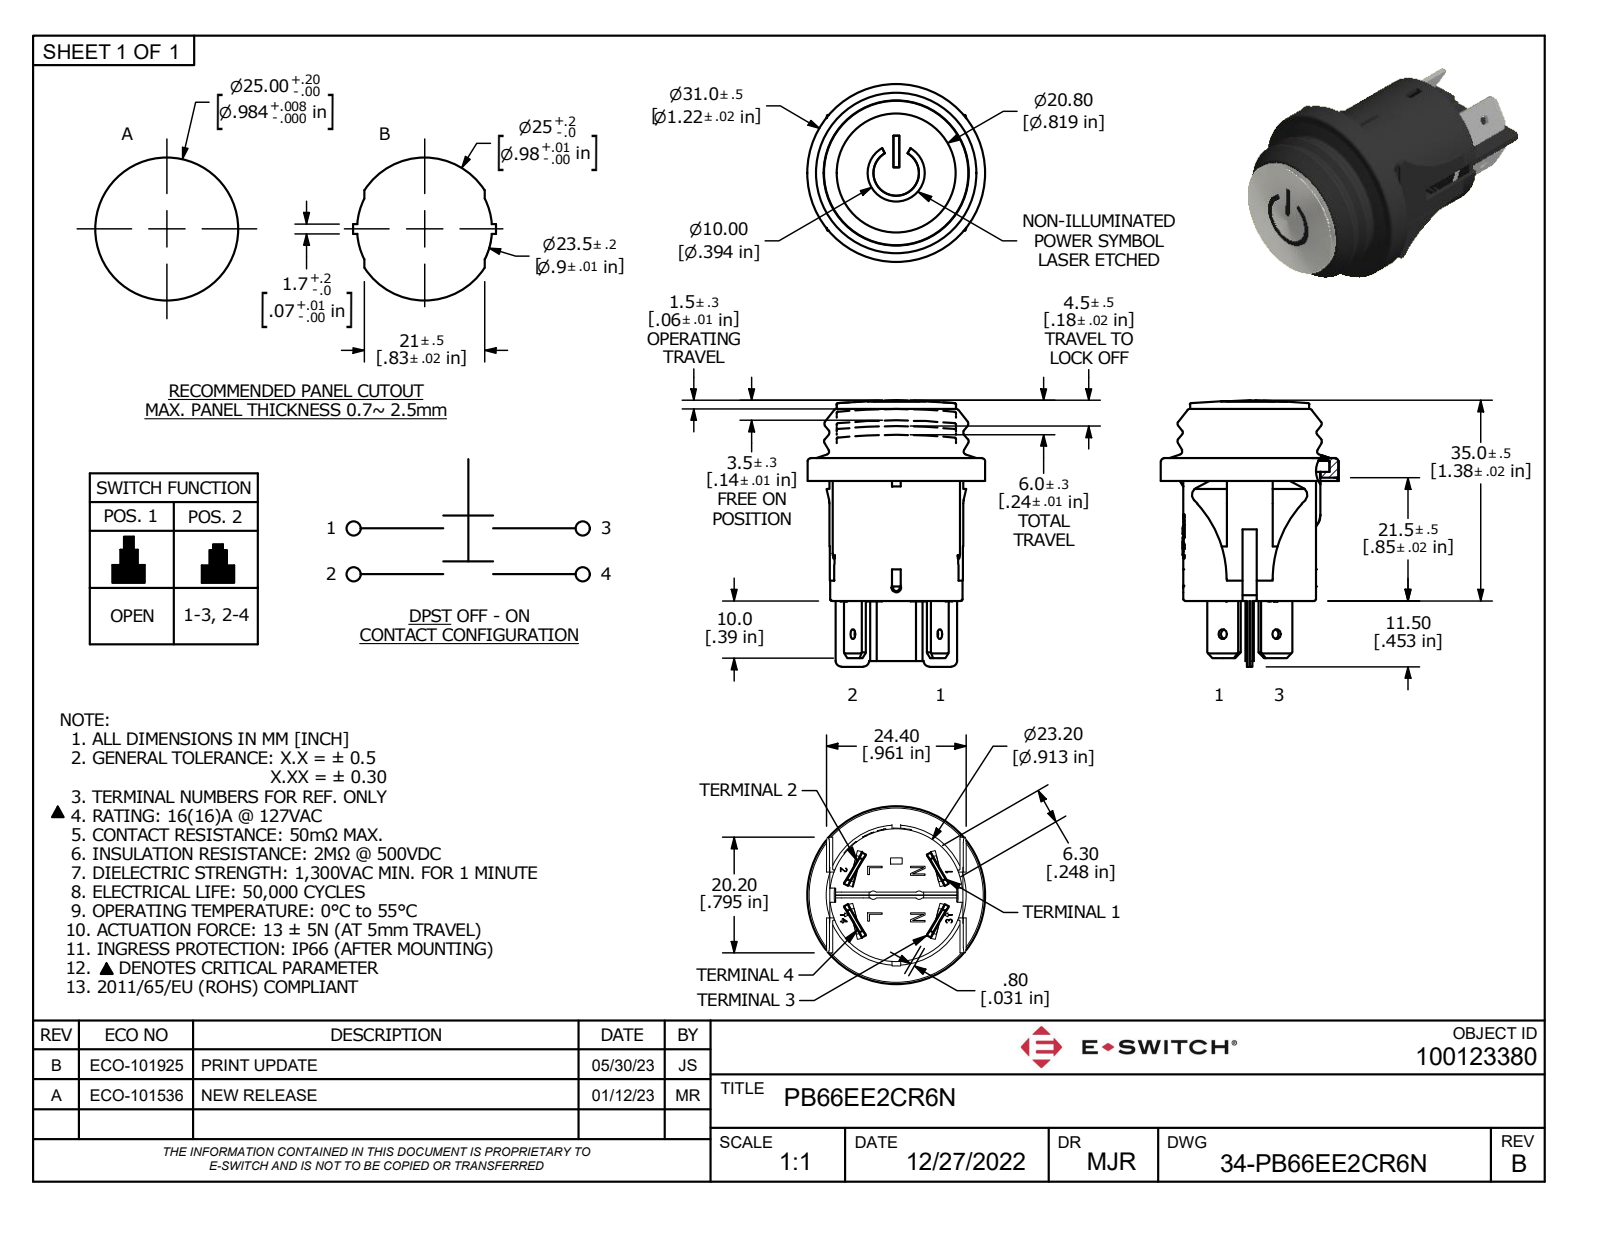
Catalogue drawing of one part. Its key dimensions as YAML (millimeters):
part_name: "PB66EE2CR6N"
step_written_by: "Autodesk Inventor 2020 (AUTOMOTIVE_DESIGN)"
units: millimeters
bodies: {solids: 1, faces: 1111, planar: 650, cylindrical: 125, other: 336}
overall_size: [46.5, 31, 31]
volume: 4156
surface_area: 9834
round_holes:
  - {diameter: 1.7, count: 4}
  - {diameter: 18, count: 1}
  - {diameter: 21.7, count: 1}
  - {diameter: 24.5, count: 1}
  - {diameter: 27.6, count: 1}
round_bosses_or_shafts:
  - {diameter: 31, count: 1}
  - {diameter: 23.2, count: 1}
  - {diameter: 20.8, count: 1}
partial_cylinders:
  - {radius: 0.25, count: 8}
  - {radius: 0.1, count: 5}
  - {radius: 0.17, count: 4}
  - {radius: 0.2, count: 4}
  - {radius: 0.42, count: 4}
  - {radius: 1, count: 4}
  - {radius: 0.75, count: 2}
  - {radius: 1.3, count: 2}
face_to_face_distances: [1, 0.47, 0.53, 21.5, 11.9, 33.4, 32.4, 20.5, 0.8, 8.9]
hole_center_spacings: [0.56]
